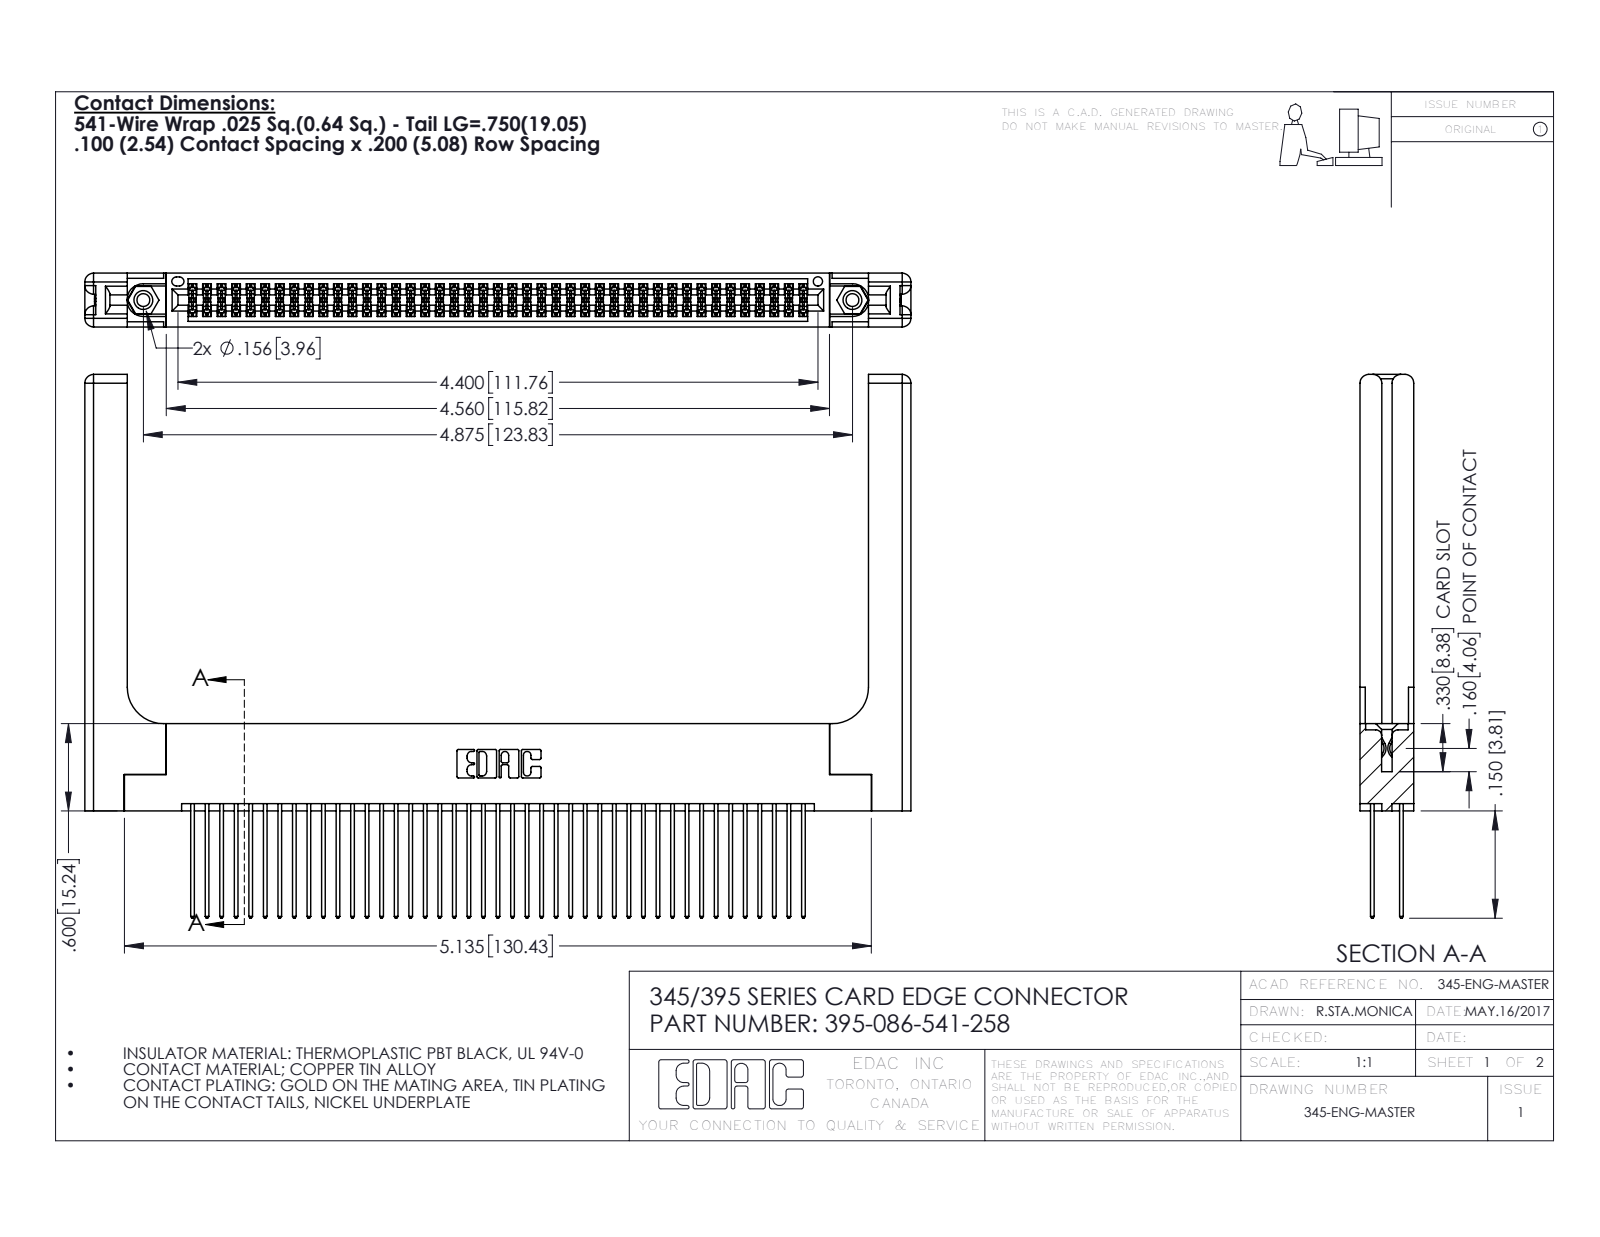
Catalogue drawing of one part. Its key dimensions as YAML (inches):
part_name: "345-250-001_345-250-001-102; 345 Part_Flush Mounting Lugs - 0.156 Dia-TH; 345-220-058_345-220-058; 395-086-541-258 (+1 more)"
step_written_by: "SolidWorks 2016 (CONFIG_CONTROL_DESIGN)"
units: inches
bodies: {solids: 91, faces: 4682, planar: 3066, cylindrical: 1556, other: 60}
overall_size: [5.679, 3.737, 0.37]
volume: 1.403
surface_area: 44.72
round_holes:
  - {diameter: 0.089, count: 2}
  - {diameter: 0.125, count: 2}
  - {diameter: 0.156, count: 2}
  - {diameter: 0.064, count: 1}
round_bosses_or_shafts:
  - {diameter: 0.155, count: 2}
partial_cylinders:
  - {radius: 0.006, count: 129}
  - {radius: 0.01, count: 86}
  - {radius: 0.01, count: 22}
  - {radius: 0.06, count: 16}
  - {radius: 0.007, count: 6}
  - {radius: 0.031, count: 6}
  - {radius: 0.026, count: 3}
  - {radius: 0.014, count: 2}
face_to_face_distances: [0.072, 0.298, 0.2, 0.37, 0.098, 0.272, 0.025, 0.225, 0.175, 0.148]
hole_center_spacings: [0.27, 4.639, 4.875]
